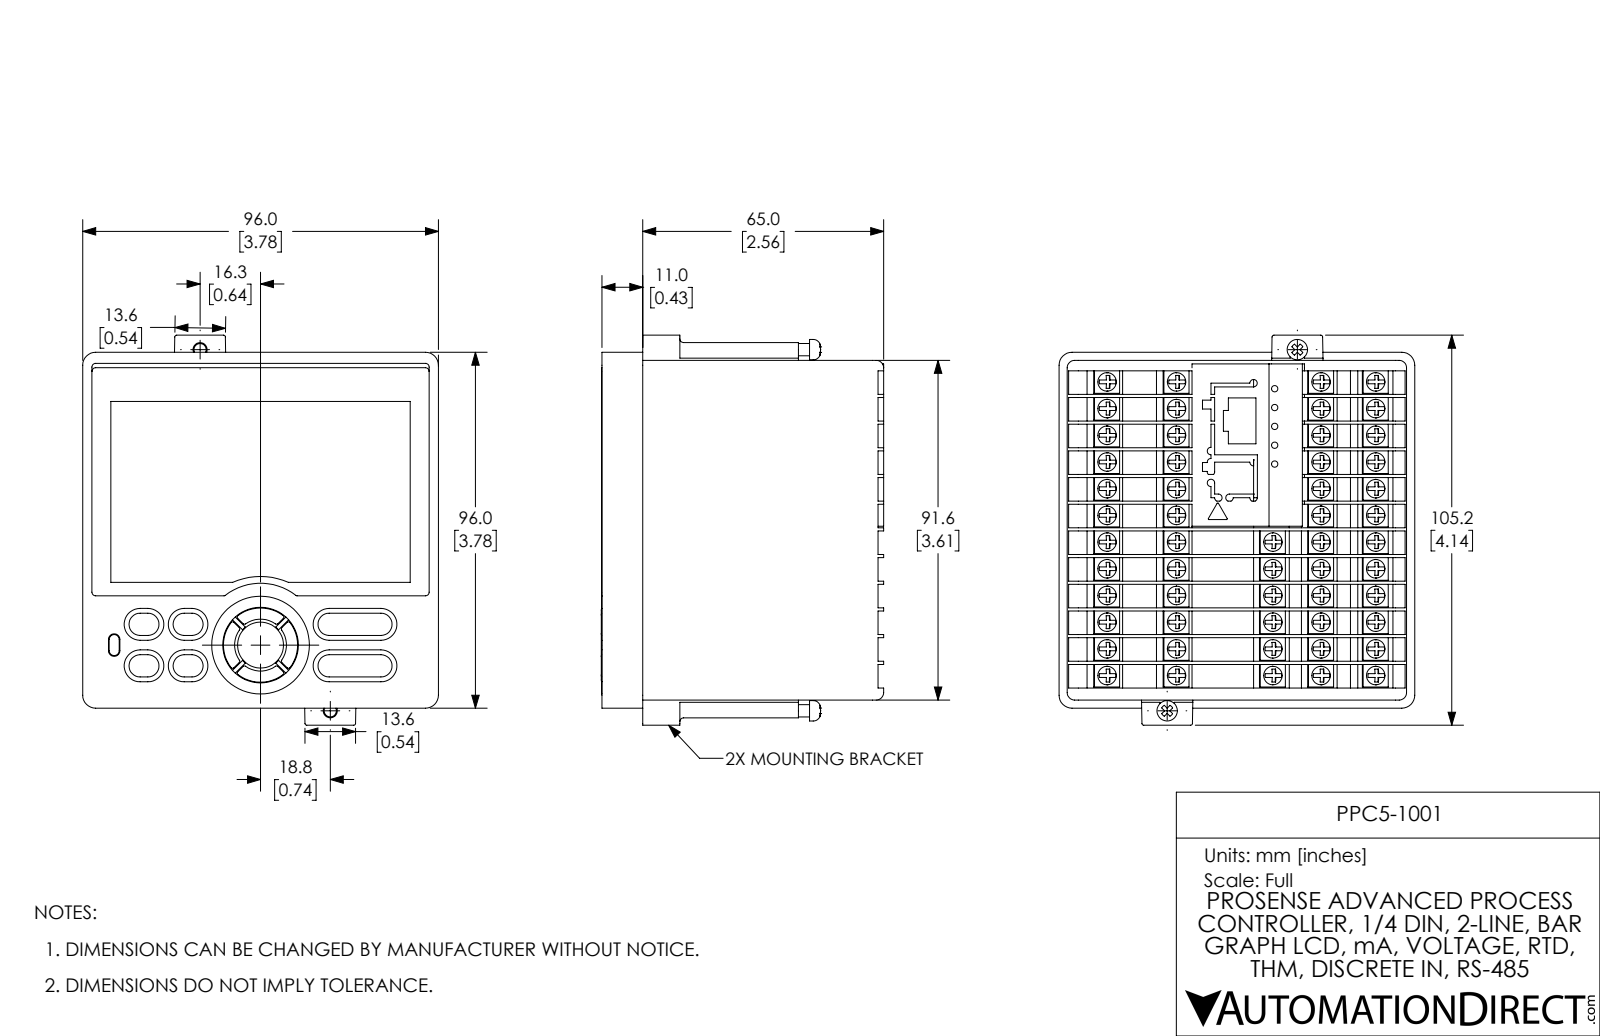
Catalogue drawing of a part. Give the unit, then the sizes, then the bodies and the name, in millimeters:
Units: millimetres
Overall size (bounding box): 105.2 × 96 × 76.2
Round holes (diameter × count): ⌀1.7 ×5, ⌀3.3 ×2, ⌀3.8 ×2, ⌀20.39 ×1
Round bosses / shafts (diameter × count): ⌀5 ×54, ⌀5.5 ×2, ⌀26.36 ×1
Partial cylindrical surfaces — rounded edges, fillets, slot ends (radius × count): R1 ×18, R0.5 ×16, R4.3 ×12, R1.5 ×10, R2 ×6, R3.5 ×4, R0.2 ×3, R1.54 ×2
Main face-to-face distances: 2.5, 89.1, 91.6, 86.6, 63.5, 7.2, 2.4, 65.9, 14.4, 2.2
Hole centre spacings: 5.08, 10.16, 15.24, 12.19, 16.78, 20.32, 21.59, 25.85
Volume: 128 403 mm³ · Surface area: 111 664 mm²
Bodies: 2 solids, 2601 faces (2017 planar, 418 cylindrical, 166 other)
Part name (STEP PRODUCT): PPC5-1000
STEP written by: SolidWorks 2017 (AUTOMOTIVE_DESIGN)
